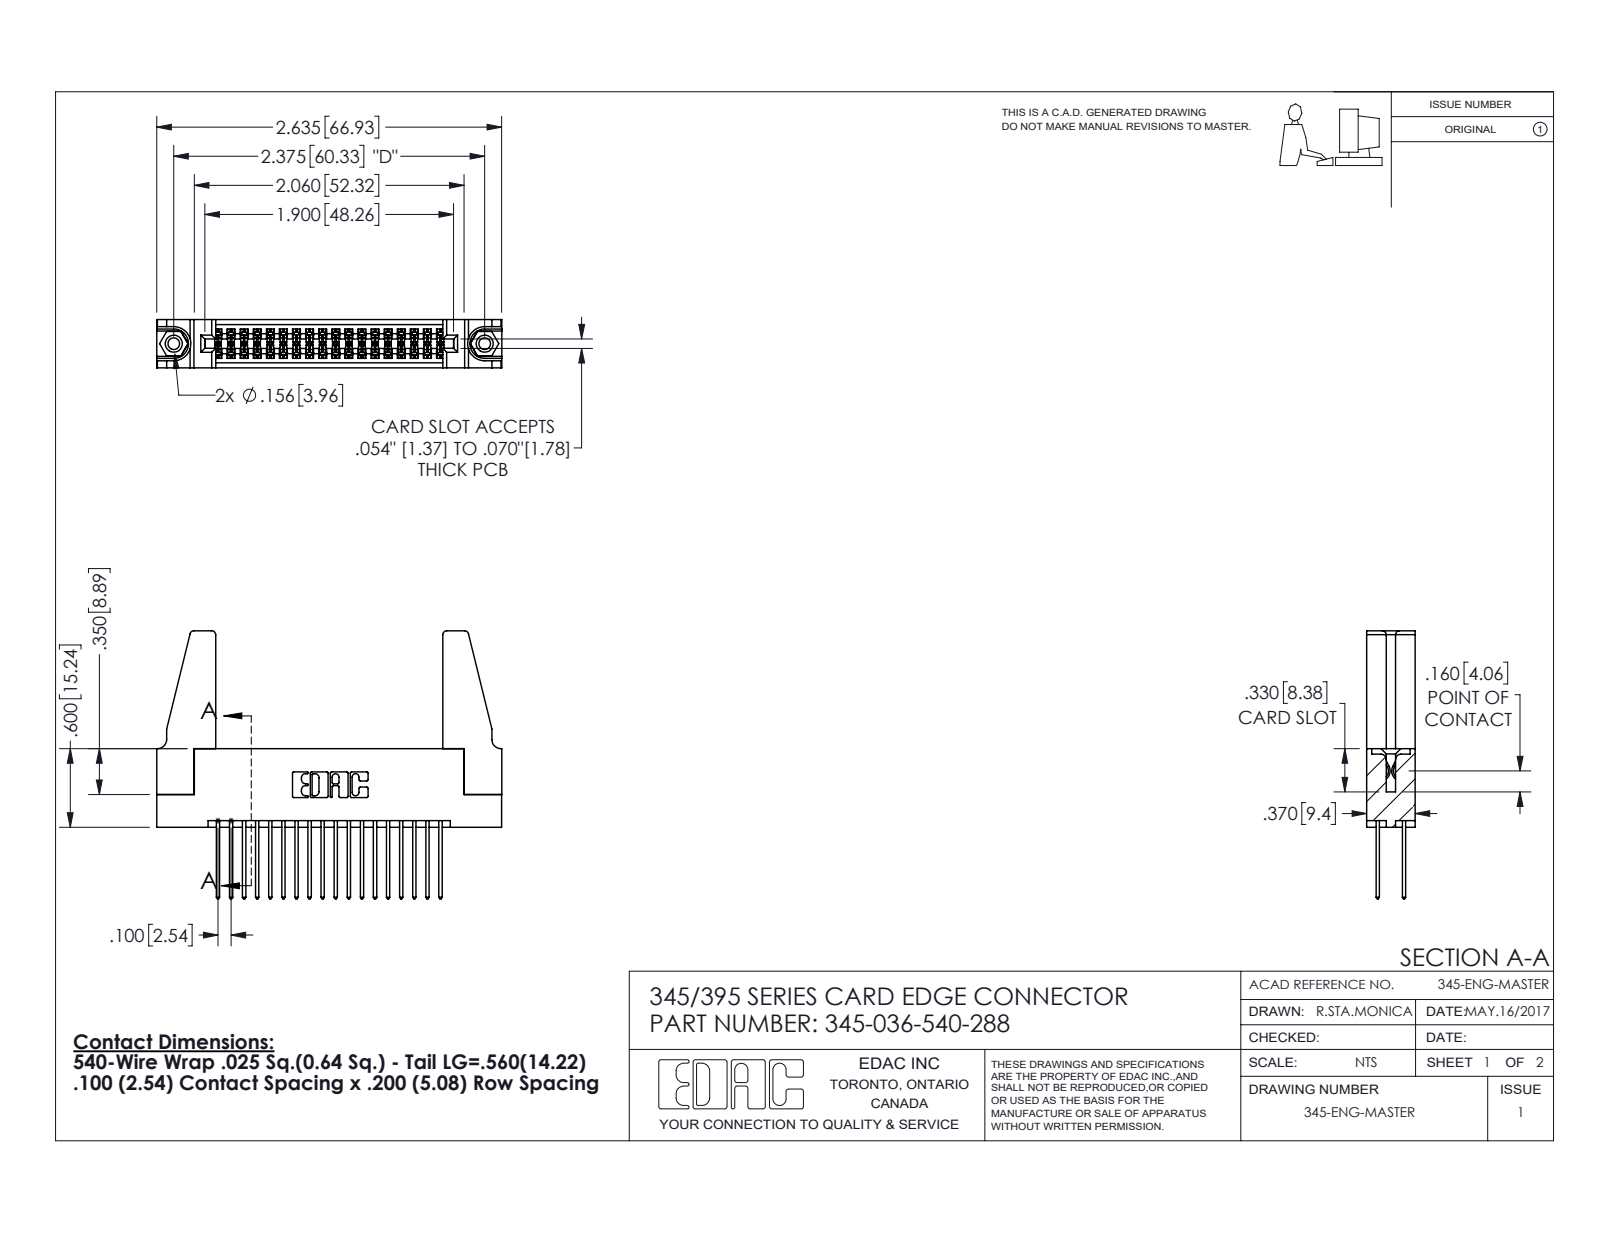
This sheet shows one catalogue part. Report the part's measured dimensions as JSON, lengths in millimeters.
{"part_name": "345-292-001_345-293-140; 345-220-078_345-220-088; 345-250-001_345-250-001-102; 345 Part_Flush Mounting Lugs - 0.156 Dia-TH (+1 more)", "step_written_by": "SolidWorks 2016 (CONFIG_CONTROL_DESIGN)", "units": "millimeters", "bodies": {"solids": 41, "faces": 2050, "planar": 1340, "cylindrical": 694, "other": 16}, "overall_size": [67, 52, 9.4], "volume_mm3": 9670, "surface_area_mm2": 12770, "round_holes": [[2.3, 2], [3.2, 2], [4, 2], [1.6, 1]], "round_bosses_or_shafts": [[3.9, 2]], "partial_cylinders_radius": [[0.2, 54], [0.3, 36], [0.3, 22], [0.8, 8], [0.2, 6], [0.8, 6], [0.7, 3], [0.4, 2]], "face_to_face_distances": [1.8, 7.6, 9.4, 5.1, 2.5, 6.9, 0.6, 5.7, 4.4, 3.8], "hole_center_spacings": [6.9, 54.4, 60.3]}
